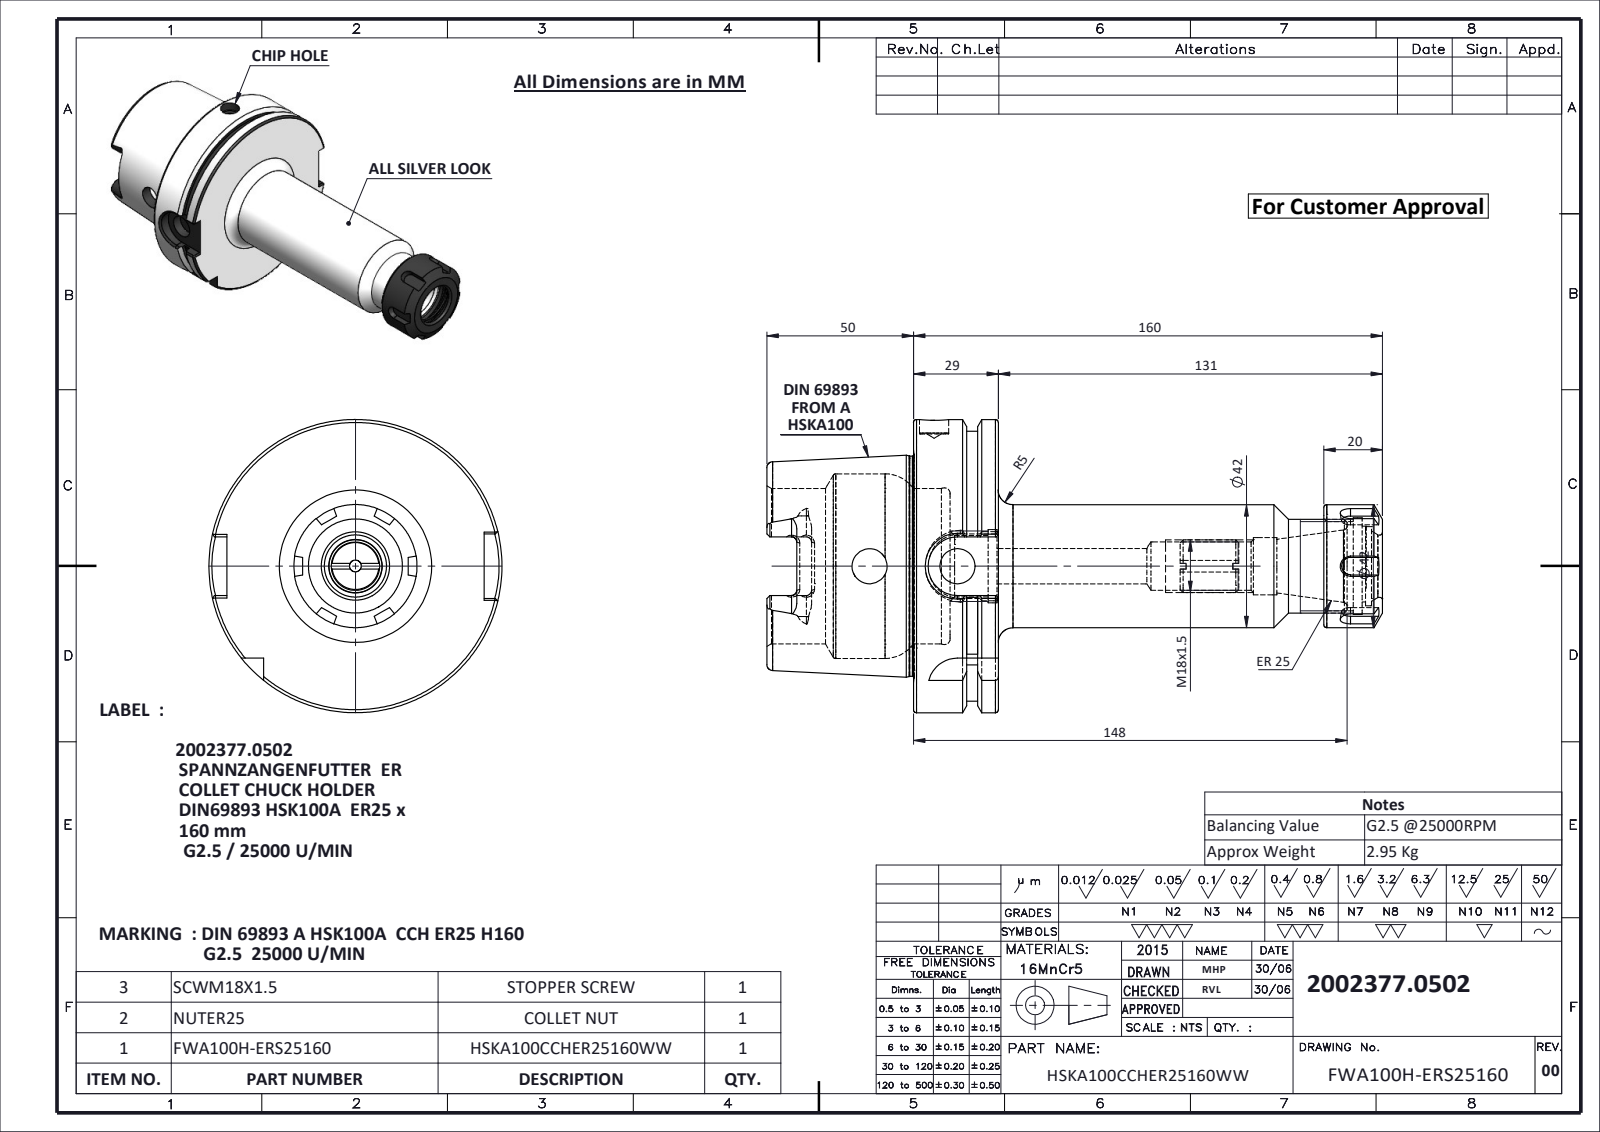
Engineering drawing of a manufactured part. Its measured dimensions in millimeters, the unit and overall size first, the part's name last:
Units: millimetres
Overall size (bounding box): 210 × 100 × 100
Round holes (diameter × count): ⌀12 ×3, ⌀4 ×1, ⌀10 ×1, ⌀16.5 ×1, ⌀19.5 ×1, ⌀21 ×1, ⌀25 ×1, ⌀25.8 ×1, ⌀27 ×1, ⌀30.5 ×1, ⌀33 ×1, ⌀53 ×1
Round bosses / shafts (diameter × count): ⌀100 ×1, ⌀92 ×1, ⌀75.16 ×1, ⌀42 ×1, ⌀32 ×1, ⌀18 ×1
Partial cylindrical surfaces — rounded edges, fillets, slot ends (radius × count): R1.8 ×6, R4.88 ×4, R10 ×2, R11 ×1
Main face-to-face distances: 28.95, 12.5, 16.45, 62.5, 50, 78.95, 20, 78.5, 124.6, 190
Hole centre spacings: 1.5, 30
Volume: 398 328 mm³ · Surface area: 78 274 mm²
Bodies: 3 solids, 260 faces (94 planar, 68 cylindrical, 98 other)
Part name (STEP PRODUCT): HSKA100CCHER25160WW; FWA100H-ERS25160; FTNUTER25; FTSCWM18X150
STEP written by: SolidWorks 2024 (CONFIG_CONTROL_DESIGN)
